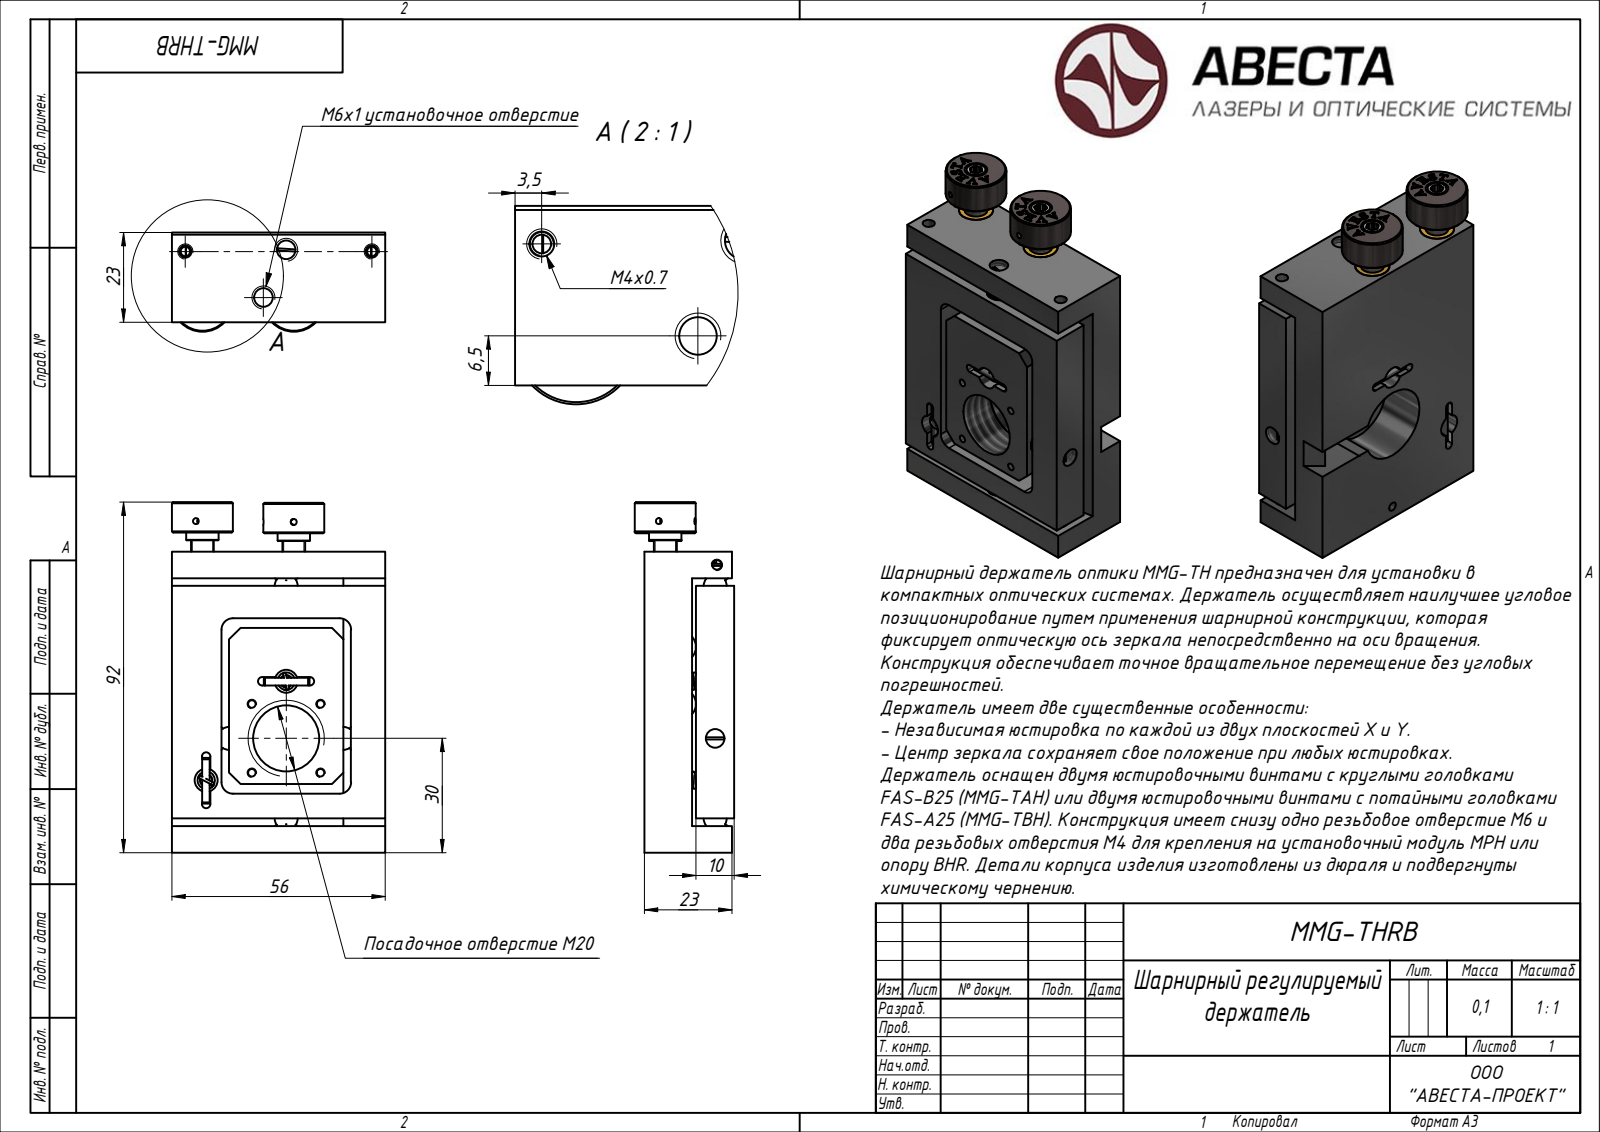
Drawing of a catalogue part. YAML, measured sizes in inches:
part_name: "MMG-TH; MMG-TH_Substitute_1; Block 01; Block 02"
step_written_by: "ST-DEVELOPER v15 (AUTOMOTIVE_DESIGN)"
units: inches
bodies: {solids: 35, faces: 916, planar: 0, cylindrical: 0, other: 916}
overall_size: [3.622, 2.205, 1.026]
